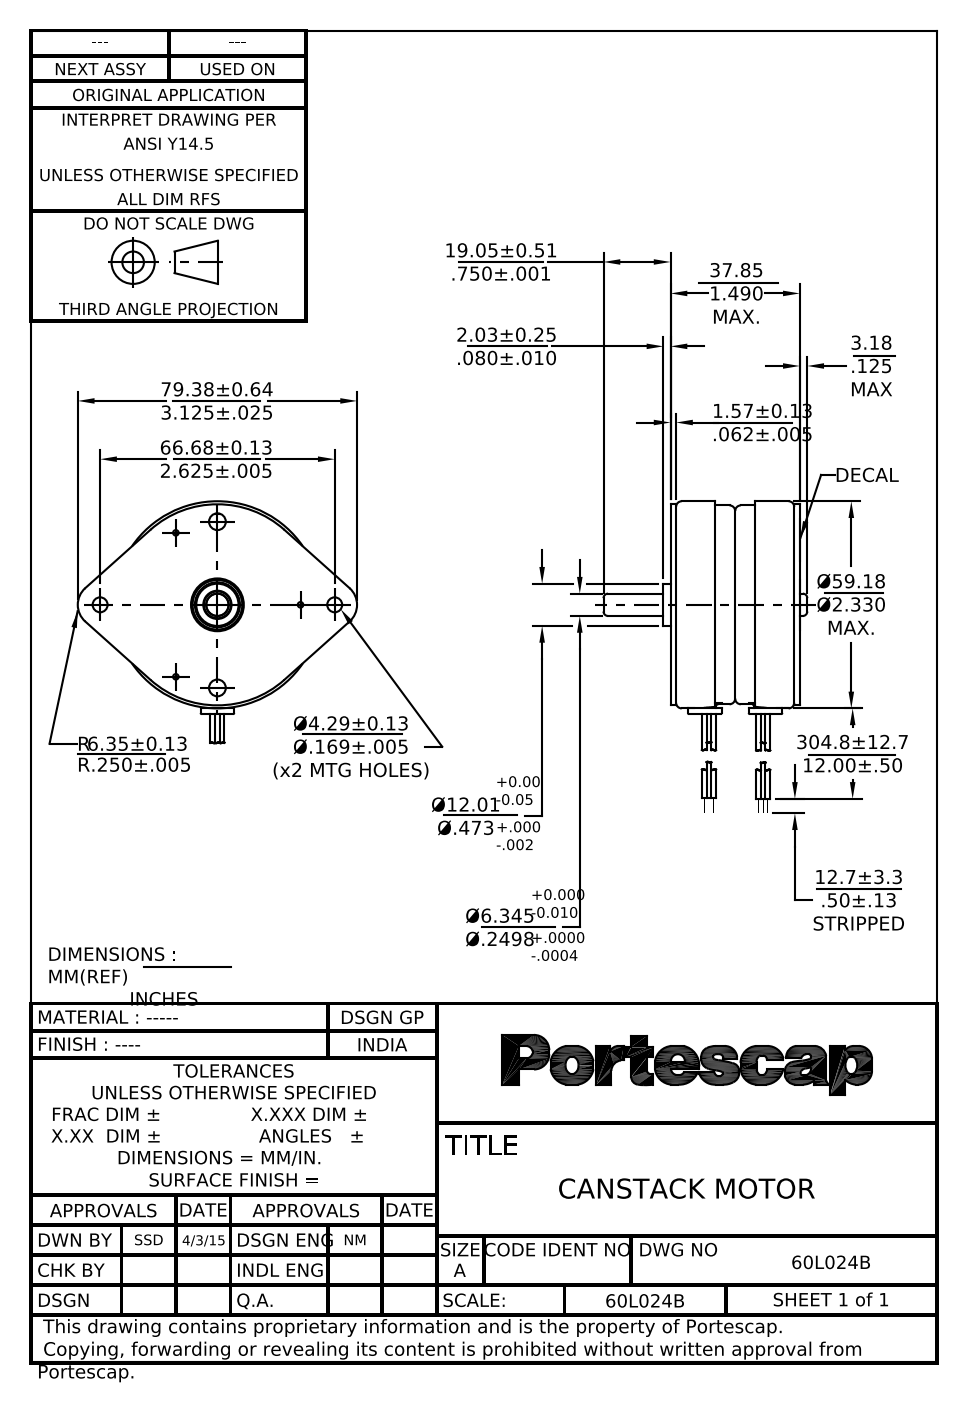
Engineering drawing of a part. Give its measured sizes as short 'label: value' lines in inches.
name: 053-0102-001_2; 149-0054-001_1; 584-0207-001_ASM_1_ASM; 012-6011-002_2 (+8 more)
written by: PRO/ENGINEER BY PARAMETRIC TECHNOLOGY CORPORATION, 2014310 (CONFIG_CONTROL_DESIGN)
unit: in
bodies: 18 solids, 227 faces (63 planar, 94 cylindrical, 70 other)
size: 3.125 × 2.843 × 2.28
volume: 5.888 in³; area: 66.5 in²
holes: 2× ⌀0.169, 2× ⌀0.187, 2× ⌀0.187, 2× ⌀0.188, 1× ⌀0.25, 1× ⌀0.3, 1× ⌀0.56, 1× ⌀2.066, 1× ⌀2.101, 1× ⌀2.129, 1× ⌀2.222
bosses: 4× ⌀0.058, 2× ⌀0.375, 2× ⌀0.25, 1× ⌀2.318, 1× ⌀2.25, 1× ⌀2.225, 1× ⌀0.56, 1× ⌀0.472
rounds: 4× R0.039, 4× R0.05, 2× R0.25
face distances: 0.062, 1.354, 1.292, 1.416, 0.044, 0.018, 1.31, 1.372, 0.646, 0.44
hole spacings: 1.609, 0.93, 1.313, 0.636, 1.86, 2.625
